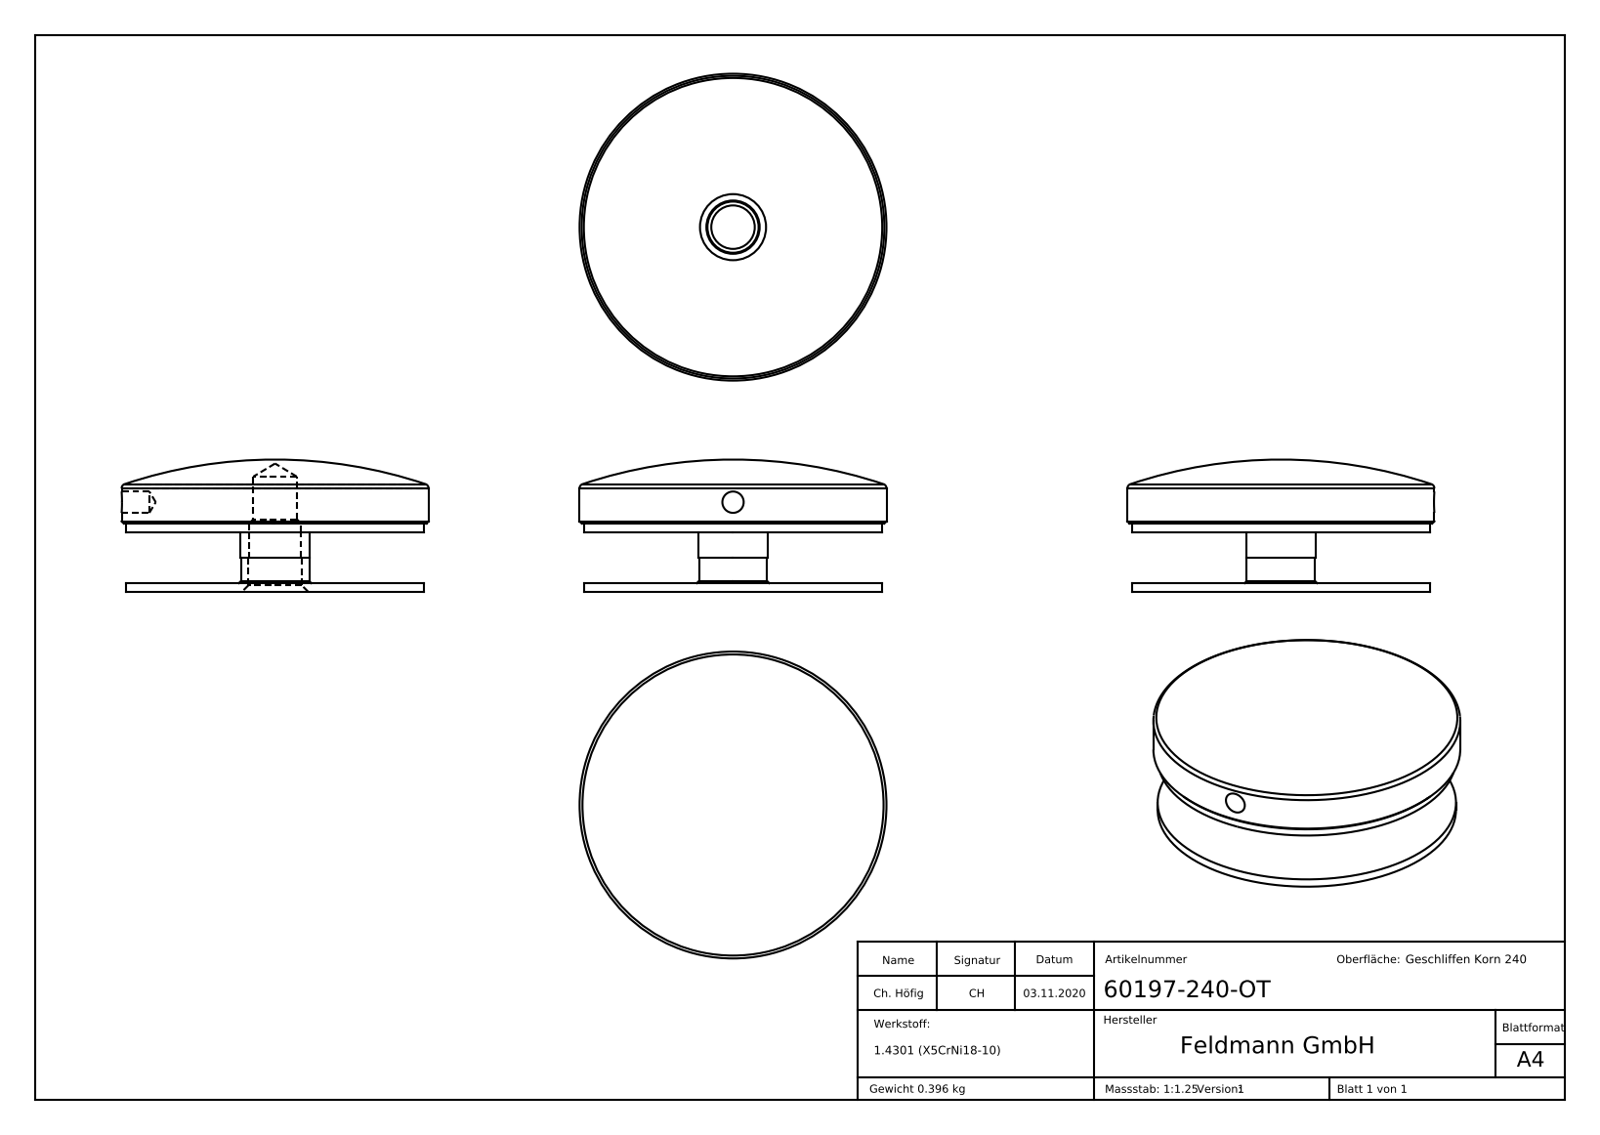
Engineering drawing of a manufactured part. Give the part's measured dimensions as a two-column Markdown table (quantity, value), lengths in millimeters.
| quantity | value |
| --- | --- |
| part name | 60197-240-OT Teil4; 60197-240-OT Teil3; 60197-240-OT Teil1; 60197-240-OT Teil4_60197-240-OT Teil4 (+5 more) |
| STEP written by | SolidWorks 2018 (CONFIG_CONTROL_DESIGN) |
| units | millimeters |
| bodies | 4 solids, 278 faces (144 planar, 20 cylindrical, 114 other) |
| overall size | 72 × 72 × 31 |
| volume | 63 709 mm³ |
| surface area | 27 813 mm² |
| round holes (diameter × count) | 5 × 1, 10.2 × 1, 12 × 1, 12.5 × 1 |
| round bosses / shafts (diameter × count) | 72 × 1, 70 × 1, 16.3 × 1, 16 × 1 |
| main face-to-face distances | 2, 14, 16, 12, 8, 6, 16.1, 14.1, 8.1, 2.1 |
